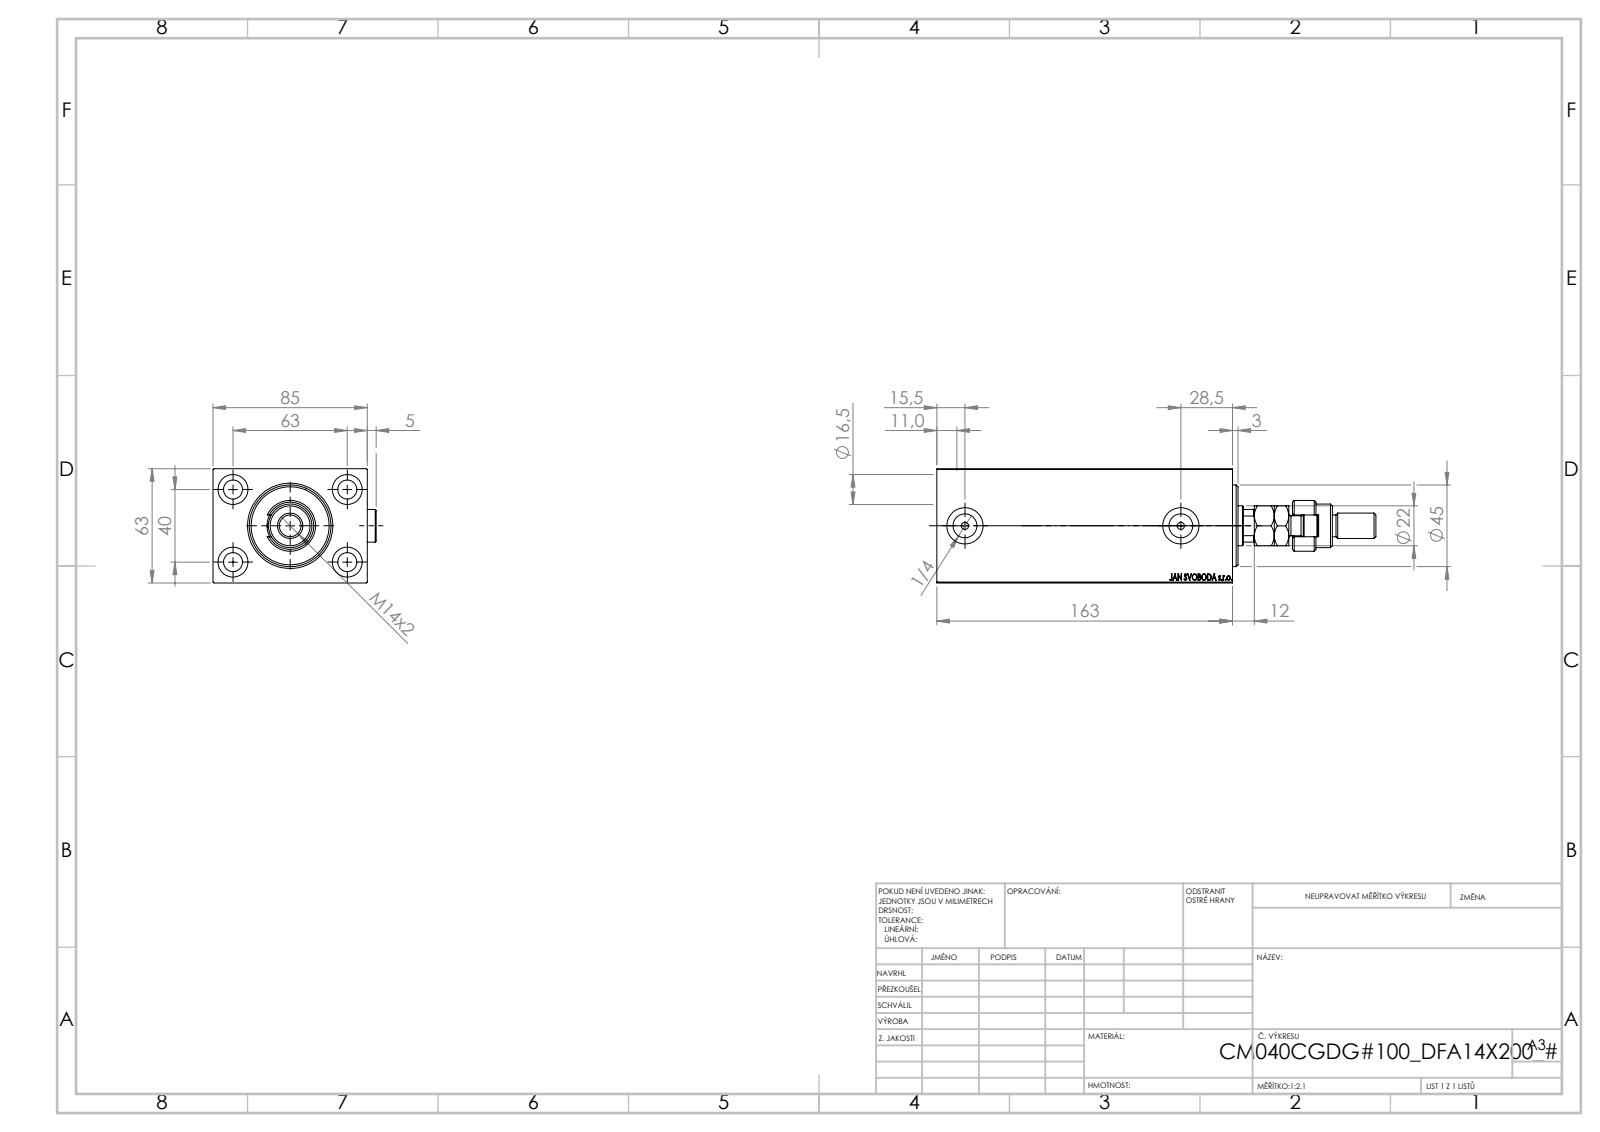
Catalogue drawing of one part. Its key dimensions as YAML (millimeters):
part_name: "V450CM_C_VCP; V450CM_VC_B; V450CM_C_Body; FEMALE_PART_FOR_DFA (+2 more)"
step_written_by: "SolidWorks 2019 (CONFIG_CONTROL_DESIGN)"
units: millimeters
bodies: {solids: 7, faces: 1001, planar: 470, cylindrical: 89, other: 442}
overall_size: [242, 89.9, 63]
volume: 738916
surface_area: 134716
round_holes:
  - {diameter: 10.5, count: 4}
  - {diameter: 16.5, count: 4}
  - {diameter: 4, count: 2}
  - {diameter: 13.16, count: 2}
  - {diameter: 20, count: 2}
  - {diameter: 12.5, count: 1}
  - {diameter: 22, count: 1}
  - {diameter: 25.5, count: 1}
  - {diameter: 40, count: 1}
  - {diameter: 42, count: 1}
  - {diameter: 45, count: 1}
round_bosses_or_shafts:
  - {diameter: 18, count: 3}
  - {diameter: 28, count: 1}
  - {diameter: 24, count: 1}
  - {diameter: 14, count: 1}
  - {diameter: 12, count: 1}
  - {diameter: 11, count: 1}
partial_cylinders:
  - {radius: 9.75, count: 1}
  - {radius: 10.5, count: 1}
face_to_face_distances: [63, 85, 12, 151, 163, 84.9, 3, 15, 139, 51]
hole_center_spacings: [37.31, 40, 63, 74.63, 119]
